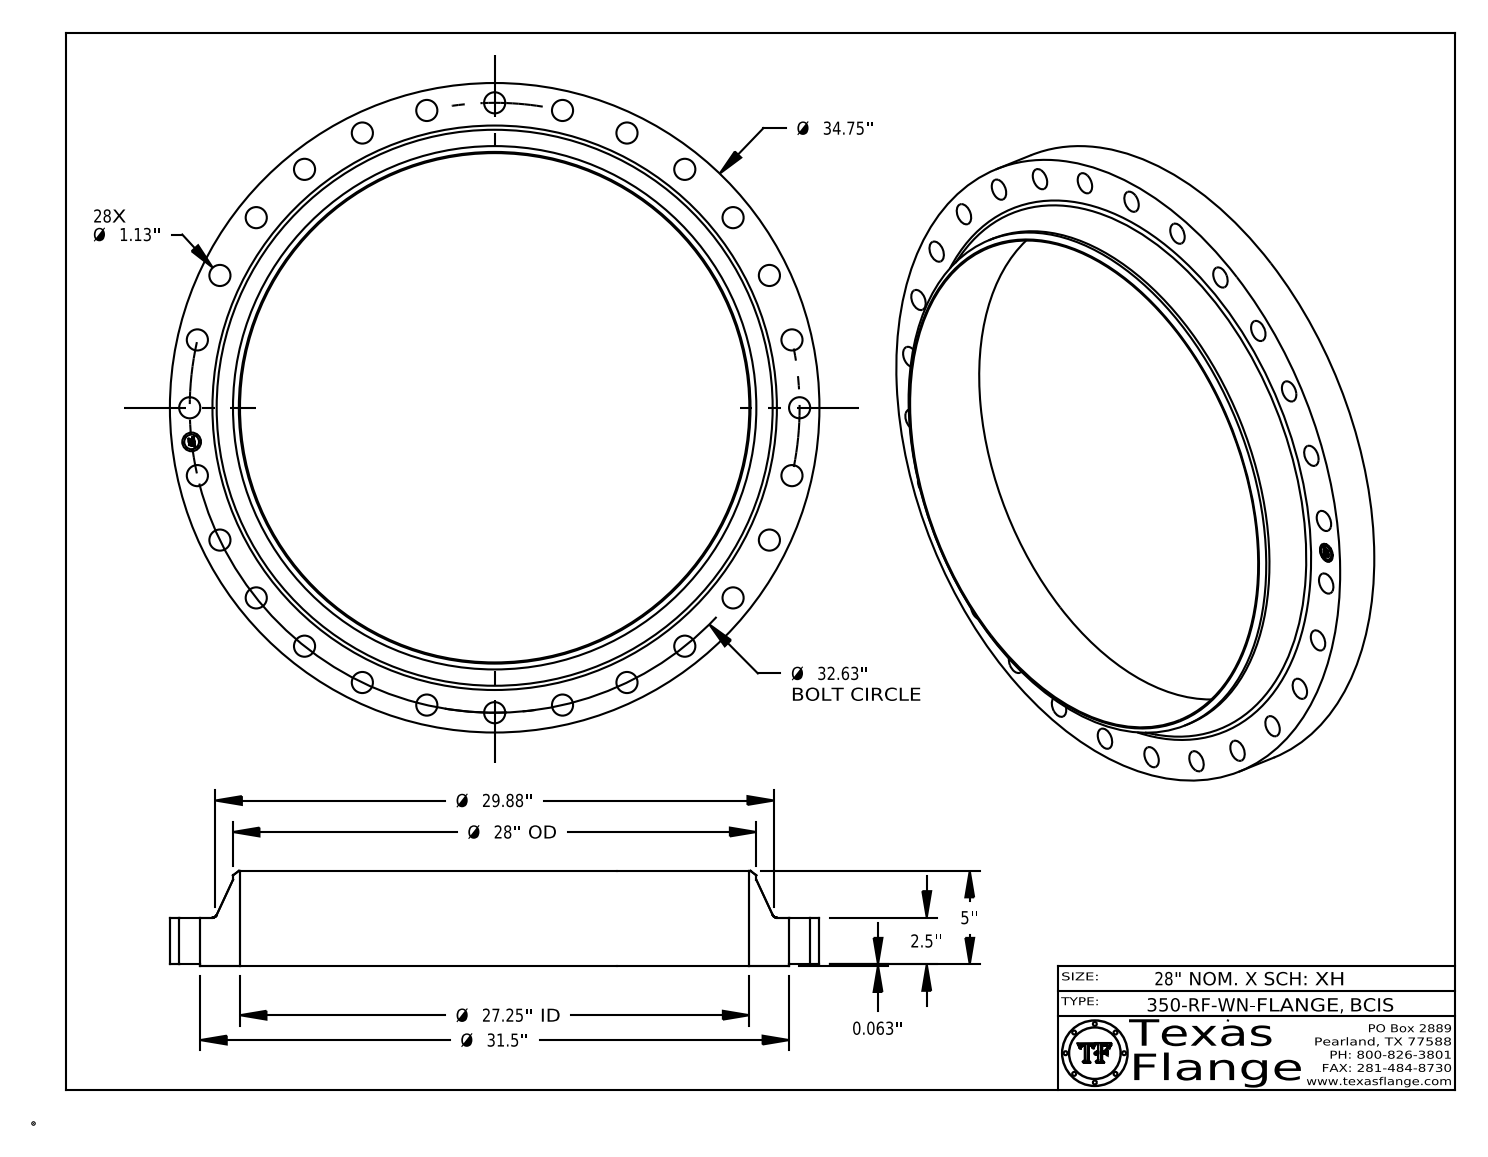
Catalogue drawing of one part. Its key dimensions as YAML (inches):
part_name: "350-RF-WN, BCIS"
step_written_by: "CATIA V5 STEP AP214 (AUTOMOTIVE_DESIGN)"
units: inches
bodies: {solids: 1, faces: 459, planar: 369, cylindrical: 84, other: 6}
overall_size: [34.75, 34.75, 5.063]
volume: 1019
surface_area: 1777
round_holes:
  - {diameter: 1.13, count: 28}
  - {diameter: 1, count: 1}
  - {diameter: 27.25, count: 1}
round_bosses_or_shafts:
  - {diameter: 0.061, count: 8}
  - {diameter: 34.75, count: 1}
  - {diameter: 31.5, count: 1}
  - {diameter: 28, count: 1}
  - {diameter: 0.788, count: 1}
face_to_face_distances: [2.563, 2.5, 0.063, 5.063, 5, 0.015, 2.548, 2.485, 2.515, 0.298]
hole_center_spacings: [14.157, 16.315, 23.073, 25.511, 27.628, 29.398, 20.344, 7.261]
